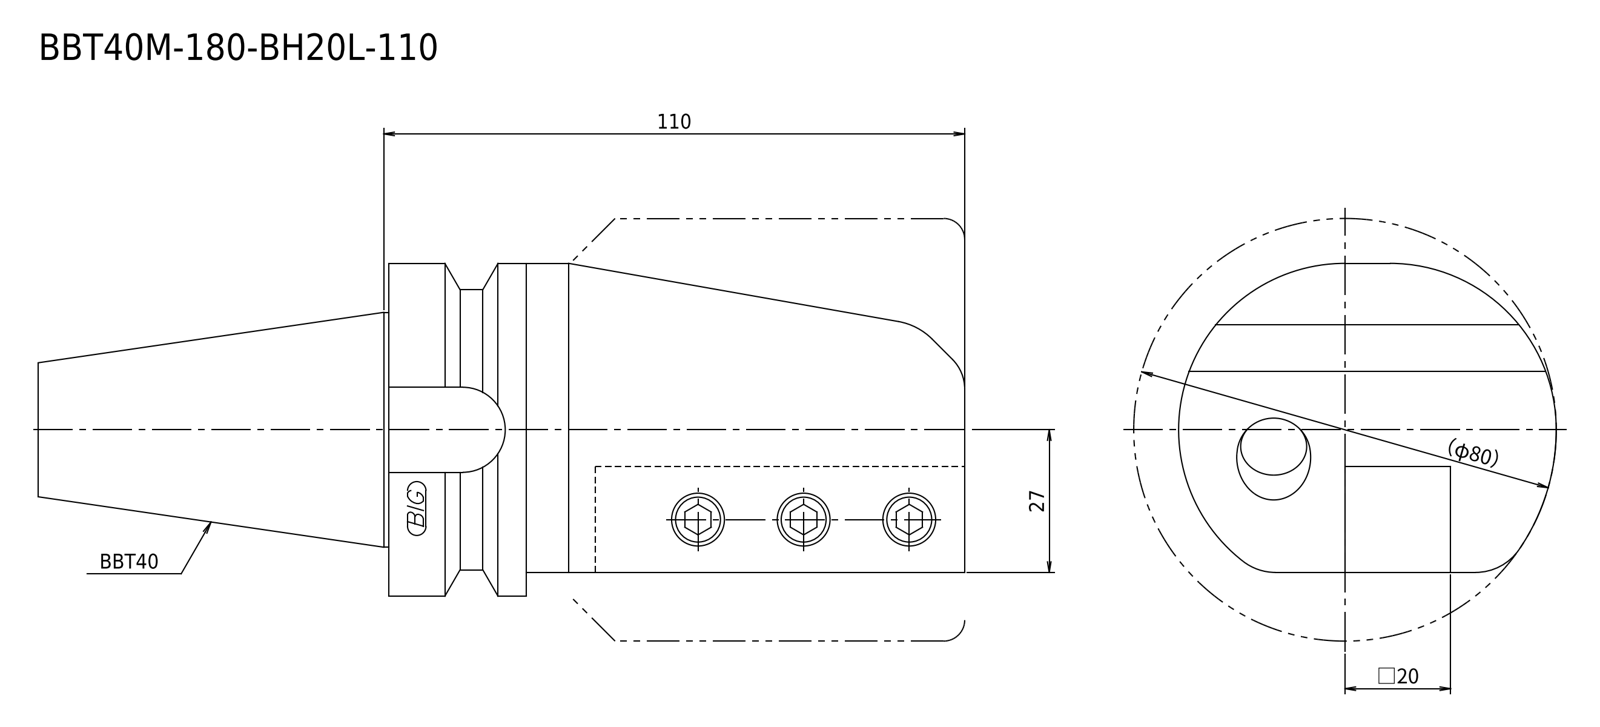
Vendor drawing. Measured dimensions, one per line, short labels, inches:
written by: Kubotek KeyCreator 2011 V10.0.2 (22737) (automotive_design)
unit: in
bodies: 1 solid, 22 faces (11 planar, 7 cylindrical, 4 other)
size: 6.906 × 2.815 × 2.48
volume: 23.16 in³; area: 59.93 in²
bosses: 1× ⌀2.48, 1× ⌀2.087, 1× ⌀1.75
rounds: 1× R1.24, 1× R1.575
face distances: 0.787, 4.291, 6.906, 2.614, 2.756, 1.535, 4.15, 3.268, 0.512, 1.024
